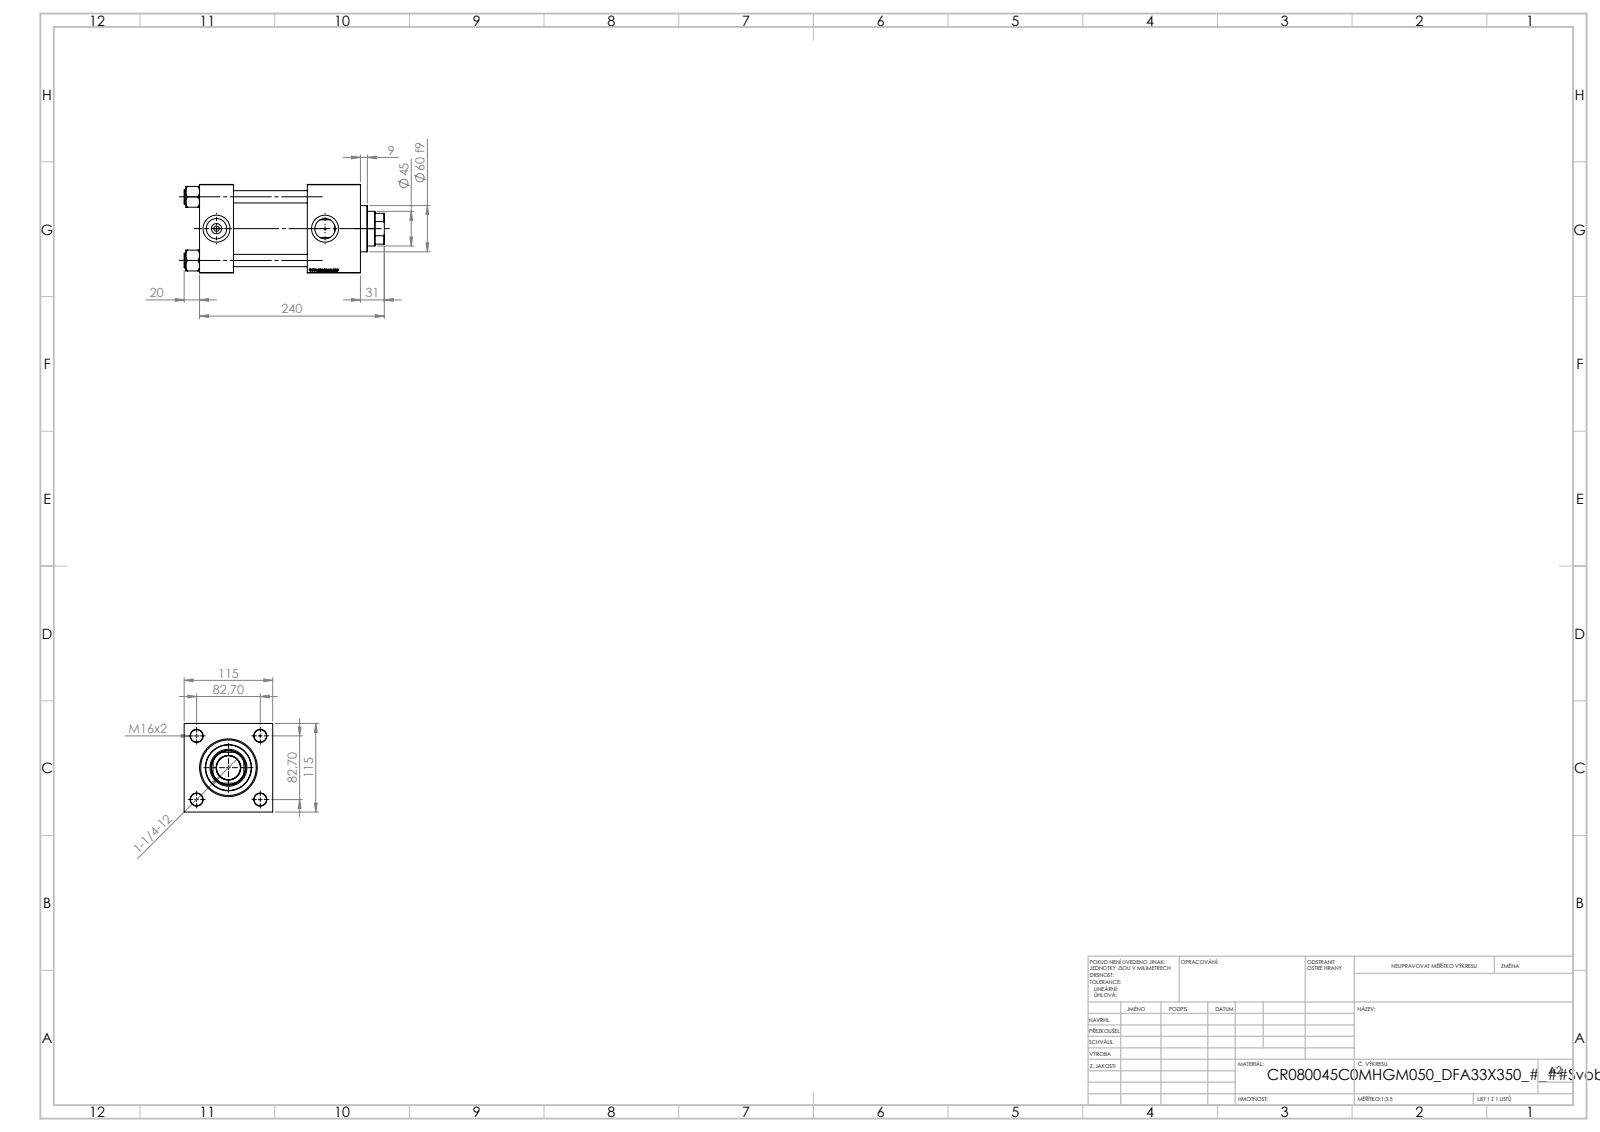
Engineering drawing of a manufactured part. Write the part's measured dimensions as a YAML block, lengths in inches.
part_name: "V215_VC_A; V215CR_C_Body; FEMALE_PART_FOR_DFA; NUT_M5_C (+2 more)"
step_written_by: "SolidWorks 2019 (CONFIG_CONTROL_DESIGN)"
units: inches
bodies: {solids: 12, faces: 1229, planar: 586, cylindrical: 95, other: 548}
overall_size: [10.236, 4.528, 4.528]
volume: 122.4
surface_area: 494
round_holes:
  - {diameter: 0.63, count: 4}
  - {diameter: 0.276, count: 2}
  - {diameter: 1.041, count: 2}
  - {diameter: 1.378, count: 2}
  - {diameter: 1.24, count: 1}
  - {diameter: 1.535, count: 1}
  - {diameter: 1.772, count: 1}
  - {diameter: 1.89, count: 1}
  - {diameter: 2.402, count: 1}
  - {diameter: 2.835, count: 1}
  - {diameter: 3.15, count: 1}
round_bosses_or_shafts:
  - {diameter: 0.748, count: 4}
  - {diameter: 3.386, count: 1}
  - {diameter: 2.362, count: 1}
  - {diameter: 2.165, count: 1}
  - {diameter: 1.811, count: 1}
  - {diameter: 1.299, count: 1}
  - {diameter: 1.22, count: 1}
partial_cylinders:
  - {radius: 0.453, count: 1}
  - {radius: 0.866, count: 1}
face_to_face_distances: [4.528, 1.732, 2.717, 8.228, 6.496, 5.512, 3.78, 1.811, 1.969, 7.098]
hole_center_spacings: [2.302, 3.256, 4.605, 5.551]
